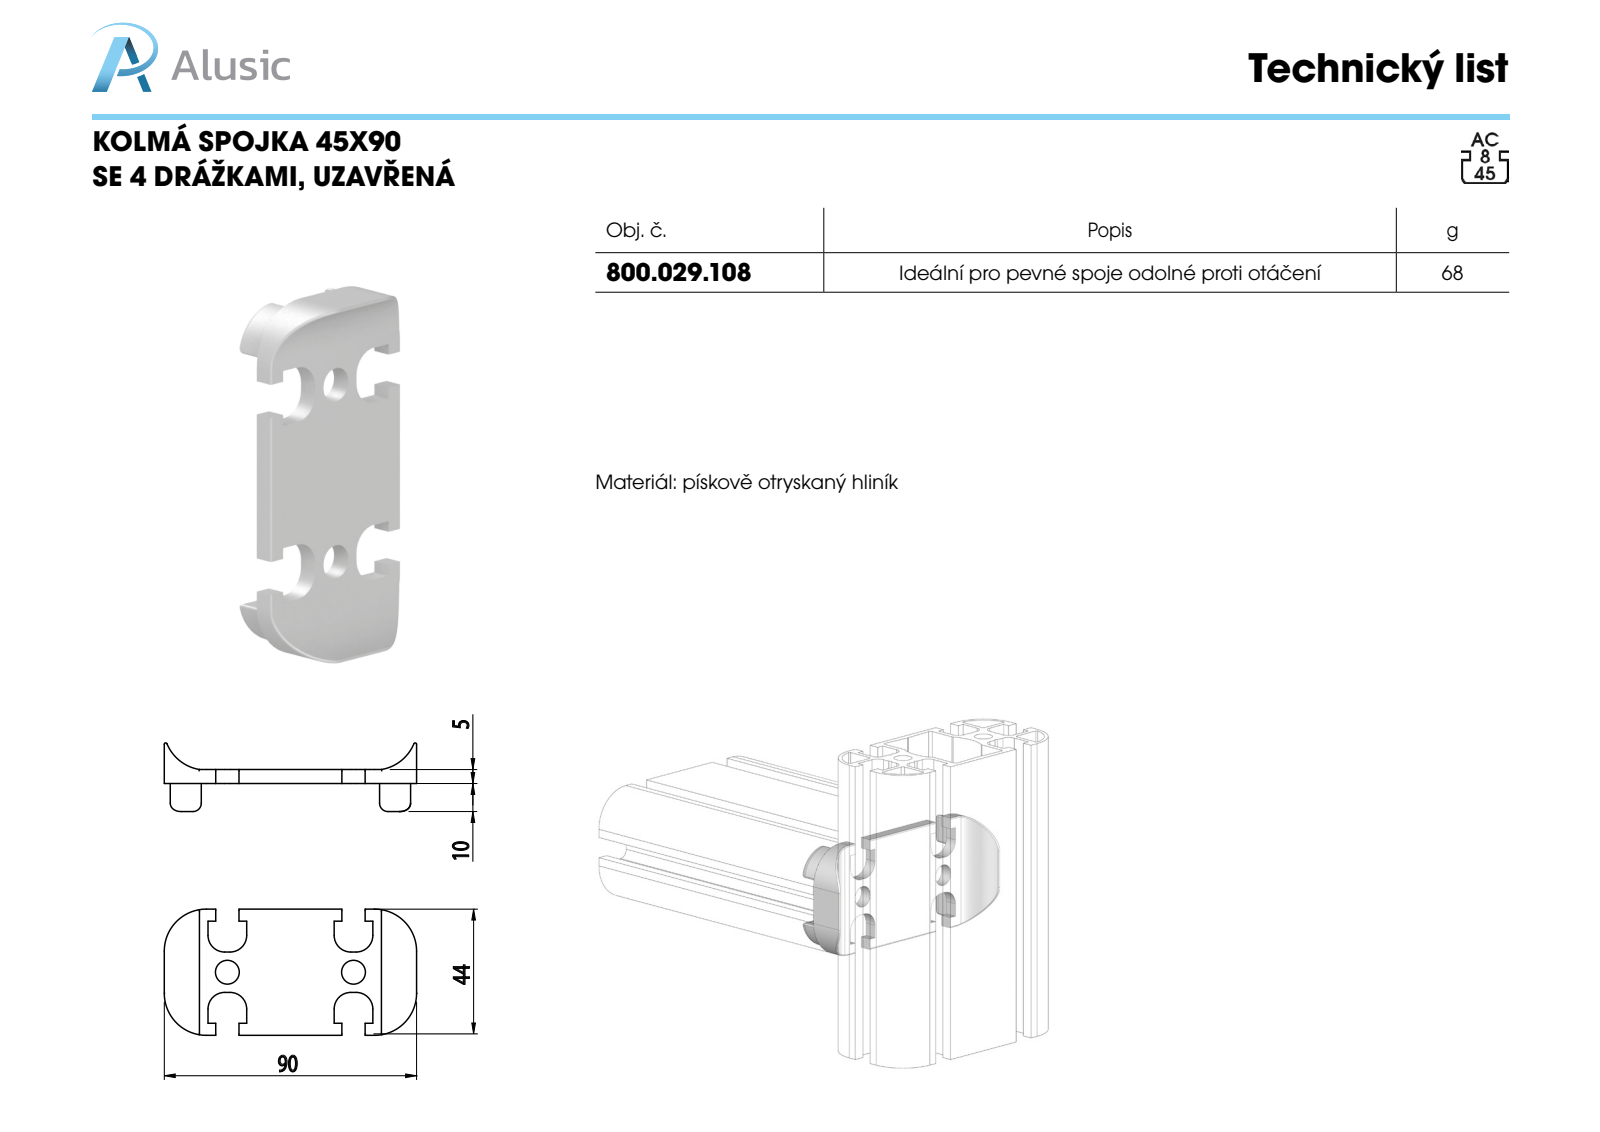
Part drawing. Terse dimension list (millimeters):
name: 800.029.108-2
written by: SolidWorks 2011 (CONFIG_CONTROL_DESIGN)
unit: mm
bodies: 1 solid, 126 faces (50 planar, 52 cylindrical, 24 other)
size: 90 × 45 × 24.48
volume: 21 333 mm³; area: 10 511 mm²
holes: 2× ⌀8.5
rounds: 12× R0.6, 8× R5.93, 4× R0.5, 4× R3, 4× R13.1, 4× R15, 2× R15.2
face distances: 5, 13.2, 45, 31.8, 76.8, 90, 2.75, 11.05, 18.6, 63.6
hole spacings: 45
